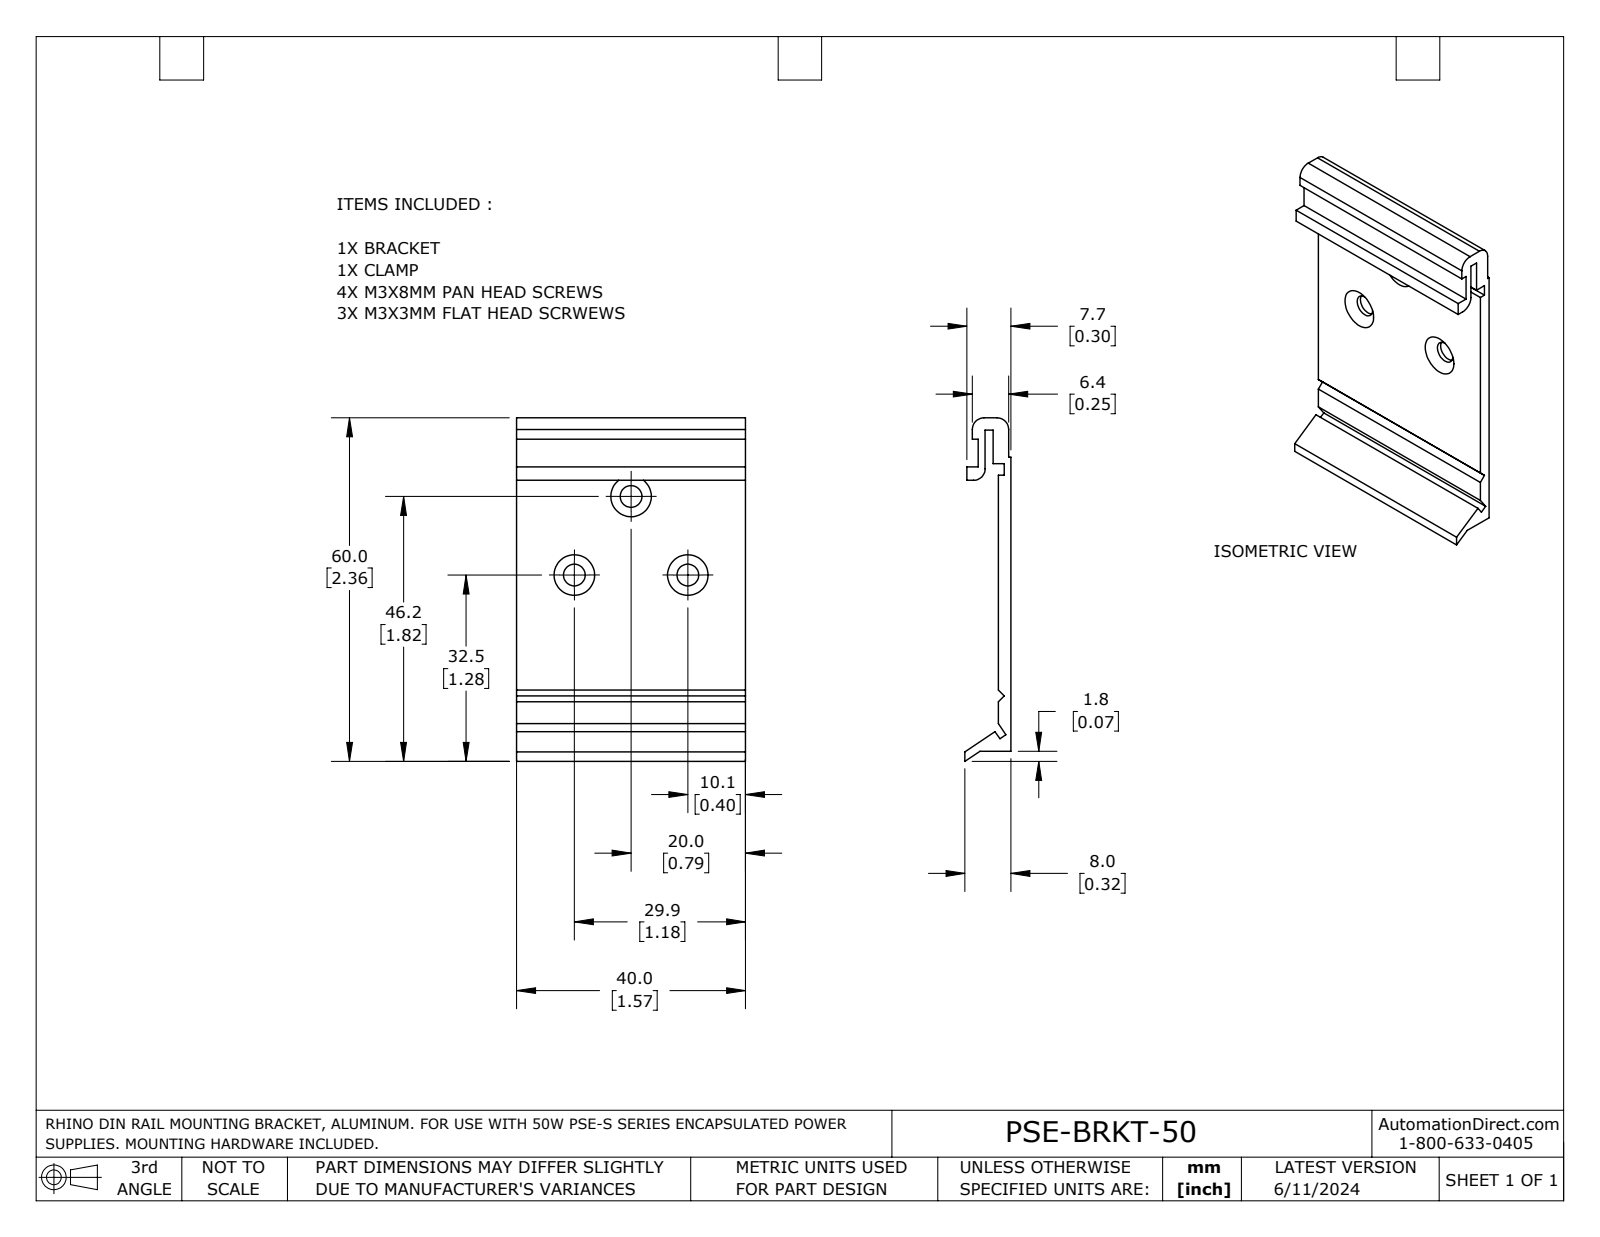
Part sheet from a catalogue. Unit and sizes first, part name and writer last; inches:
Units: inches
Overall size (bounding box): 2.361 × 1.574 × 0.317
Round holes (diameter × count): ⌀0.15 ×3
Partial cylindrical surfaces — rounded edges, fillets, slot ends (radius × count): R0.08 ×3
Main face-to-face distances: 0.086, 0.091, 0.177, 0.139, 0.055, 0.037, 0.122, 0.162, 0.107, 0.07
Hole centre spacings: 0.666, 0.78
Volume: 0.387 in³ · Surface area: 10.78 in²
Bodies: 1 solid, 38 faces (29 planar, 6 cylindrical, 3 other)
Part name (STEP PRODUCT): PSE-BRKT-50
STEP written by: SolidWorks 2023 (AUTOMOTIVE_DESIGN)
